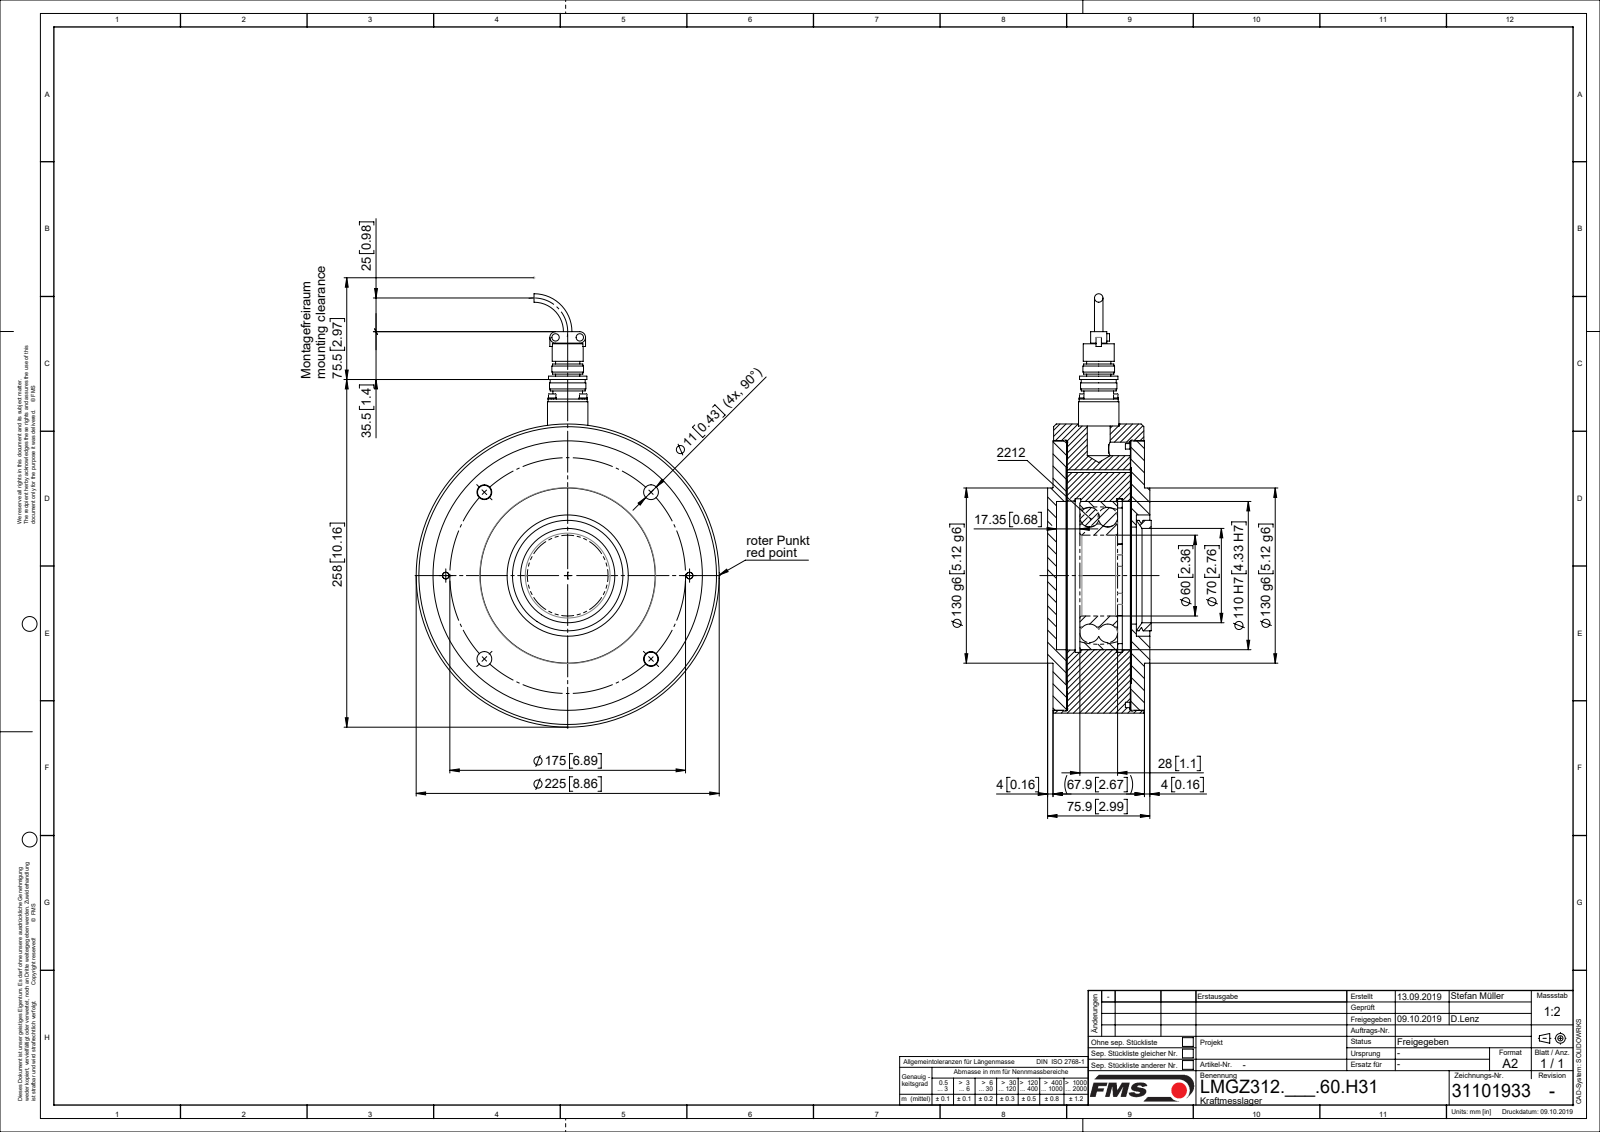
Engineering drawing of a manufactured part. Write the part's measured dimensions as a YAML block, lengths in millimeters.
part_name: "L50036; L4765504; TEIL1; L49151 (+8 more)"
step_written_by: "Mechanical Desktop 2007 (CONFIG_CONTROL_DESIGN)"
units: millimeters
bodies: {solids: 20, faces: 400, planar: 112, cylindrical: 232, other: 56}
overall_size: [321.65, 225, 75.9]
volume: 2378000
surface_area: 391814
round_holes:
  - {diameter: 11, count: 6}
  - {diameter: 2.6, count: 4}
  - {diameter: 3.2, count: 4}
  - {diameter: 3.4, count: 4}
  - {diameter: 9, count: 4}
  - {diameter: 5, count: 2}
  - {diameter: 6.6, count: 2}
  - {diameter: 23, count: 1}
  - {diameter: 60, count: 1}
  - {diameter: 70, count: 1}
  - {diameter: 72, count: 1}
  - {diameter: 88.2, count: 1}
round_bosses_or_shafts:
  - {diameter: 5.5, count: 6}
  - {diameter: 6.2, count: 4}
  - {diameter: 3, count: 4}
  - {diameter: 2.5, count: 4}
  - {diameter: 10, count: 2}
  - {diameter: 6, count: 2}
  - {diameter: 225, count: 1}
  - {diameter: 199, count: 1}
partial_cylinders:
  - {radius: 4.25, count: 2}
  - {radius: 81, count: 1}
  - {radius: 86, count: 1}
face_to_face_distances: [47.25, 10.45, 10.2, 57.45, 57.7, 47.5, 9.75, 0.5, 48, 9.7]
hole_center_spacings: [16.26, 23, 68.17, 87.5, 123.74, 164.45, 32.53, 90.5]
